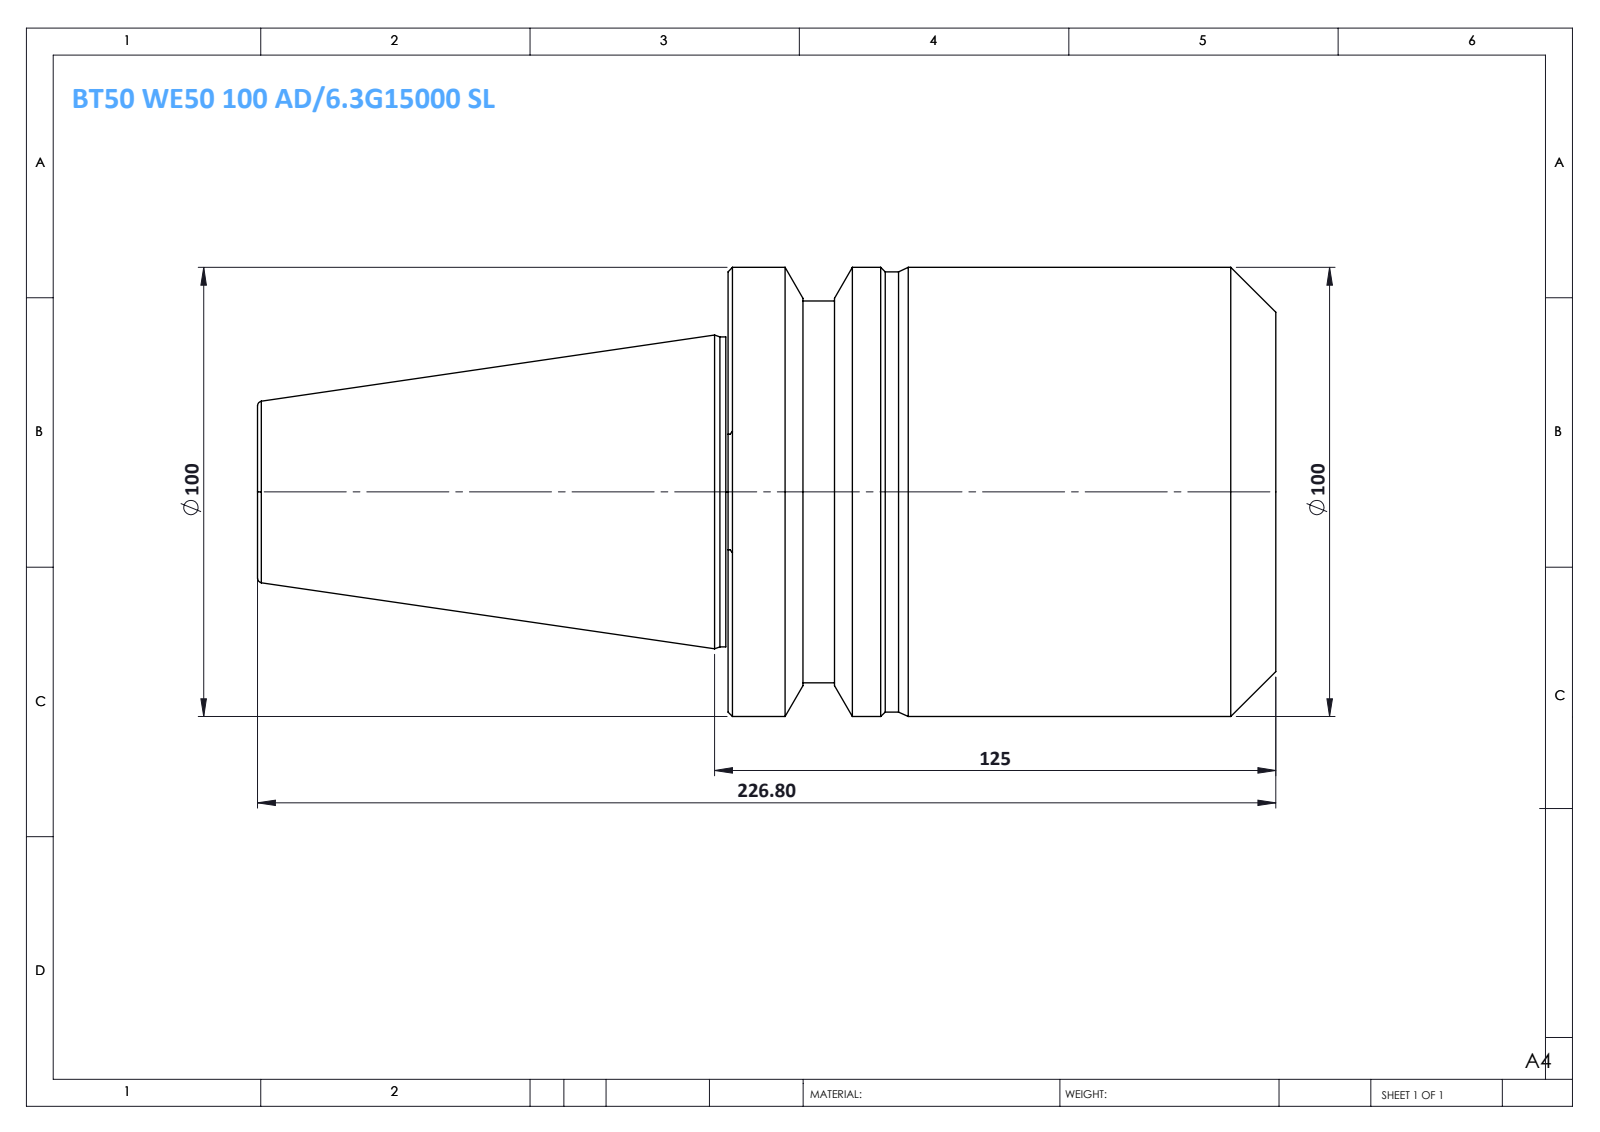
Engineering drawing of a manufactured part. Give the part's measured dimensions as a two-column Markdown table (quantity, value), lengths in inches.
| quantity | value |
| --- | --- |
| part name | BT50 WE50 125 AD-6.3G15000 SL |
| STEP written by | SolidWorks 2014 (CONFIG_CONTROL_DESIGN) |
| units | inches |
| bodies | 1 solid, 40 faces (5 planar, 12 cylindrical, 23 other) |
| overall size | 8.929 × 3.937 × 3.937 |
| volume | 71.89 in³ |
| surface area | 108.6 in² |
| round bosses / shafts (diameter × count) | 3.937 × 1, 3.858 × 1, 3.346 × 1, 2.717 × 1 |
| main face-to-face distances | 4.803, 8.929, 4.126, 4.146, 0.657, 4.783, 3.87, 0.276, 0.933, 5.059 |
